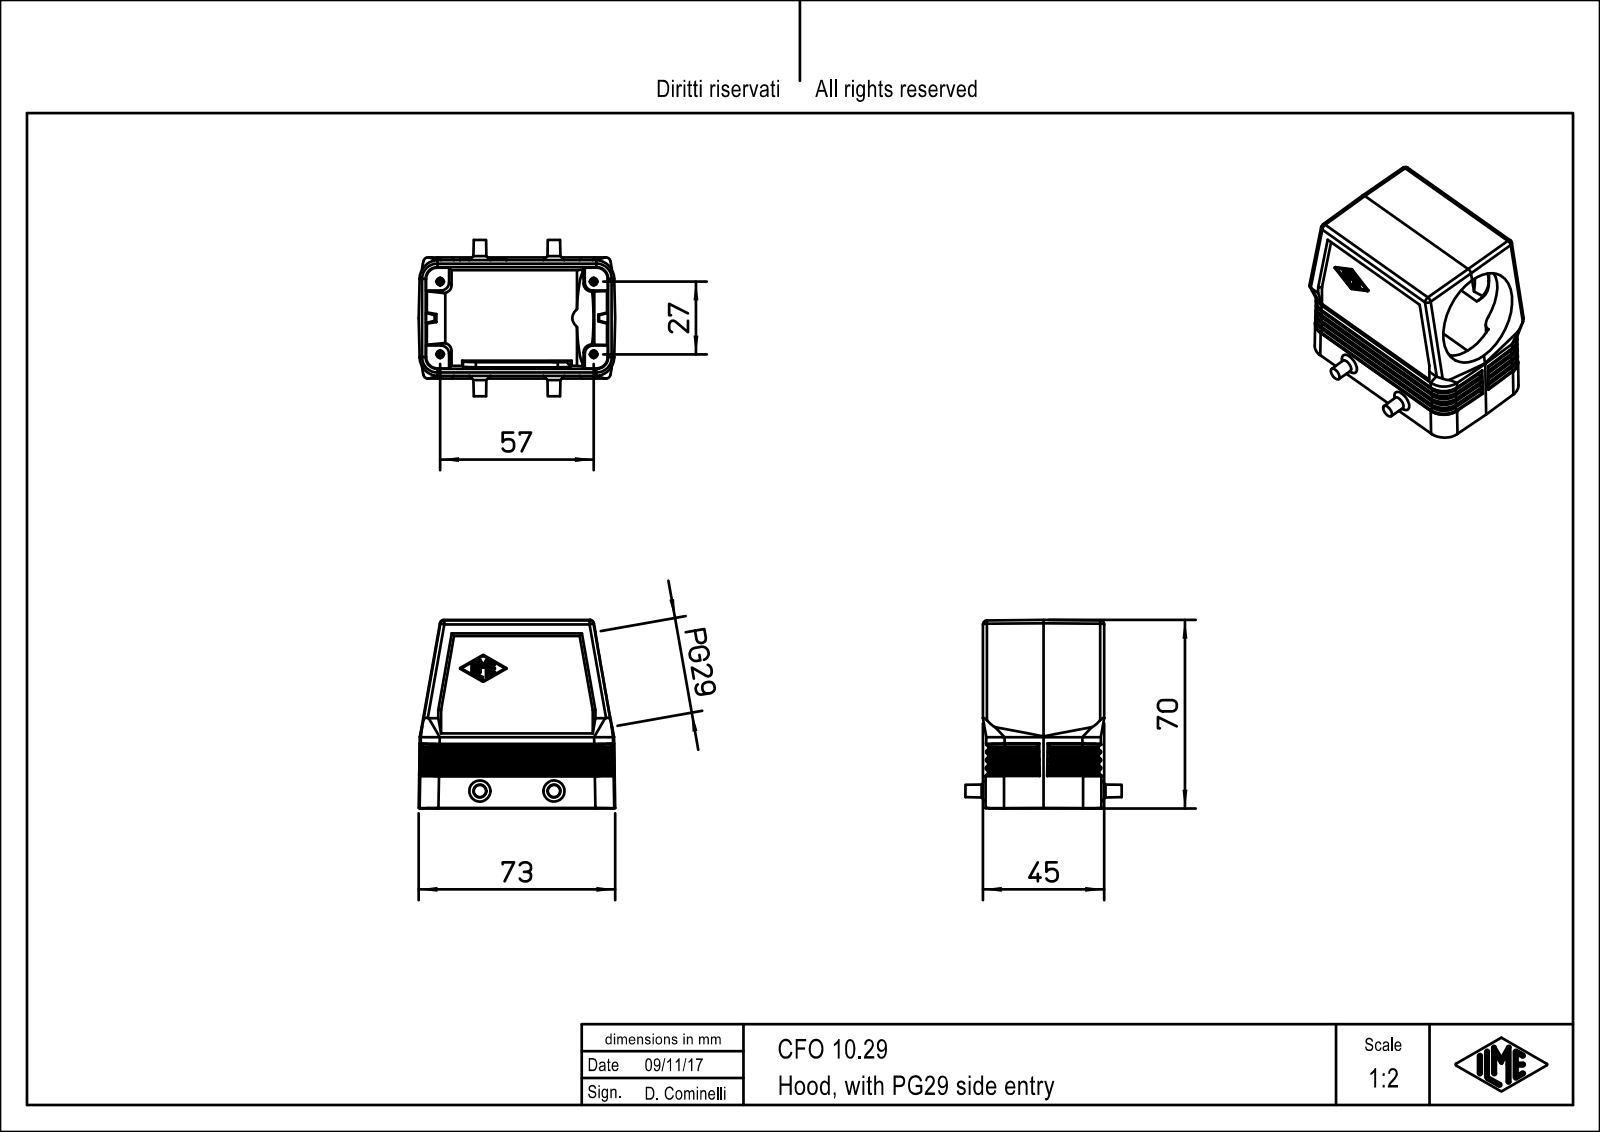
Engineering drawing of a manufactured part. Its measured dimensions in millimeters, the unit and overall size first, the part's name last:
Units: millimetres
Overall size (bounding box): 72.99 × 70 × 58
Round holes (diameter × count): ⌀35.7 ×1
Partial cylindrical surfaces — rounded edges, fillets, slot ends (radius × count): R0.5 ×16, R0.33 ×15, R1.5 ×10, R7 ×8, R3 ×4, R4.2 ×4, R0.17 ×3, R0.67 ×1
Main face-to-face distances: 43, 8.5, 2, 1.91, 44, 1, 4, 45, 6, 11.35
Volume: 63 573 mm³ · Surface area: 32 698 mm²
Bodies: 1 solid, 401 faces (172 planar, 71 cylindrical, 158 other)
Part name (STEP PRODUCT): CFO_10.29
STEP written by: PTC Creo Elements/Direct Modeling 19.0E 27-Jun-2016 (C) Parametric Technology GmbH (AUTOMOTIVE_DESIGN)
